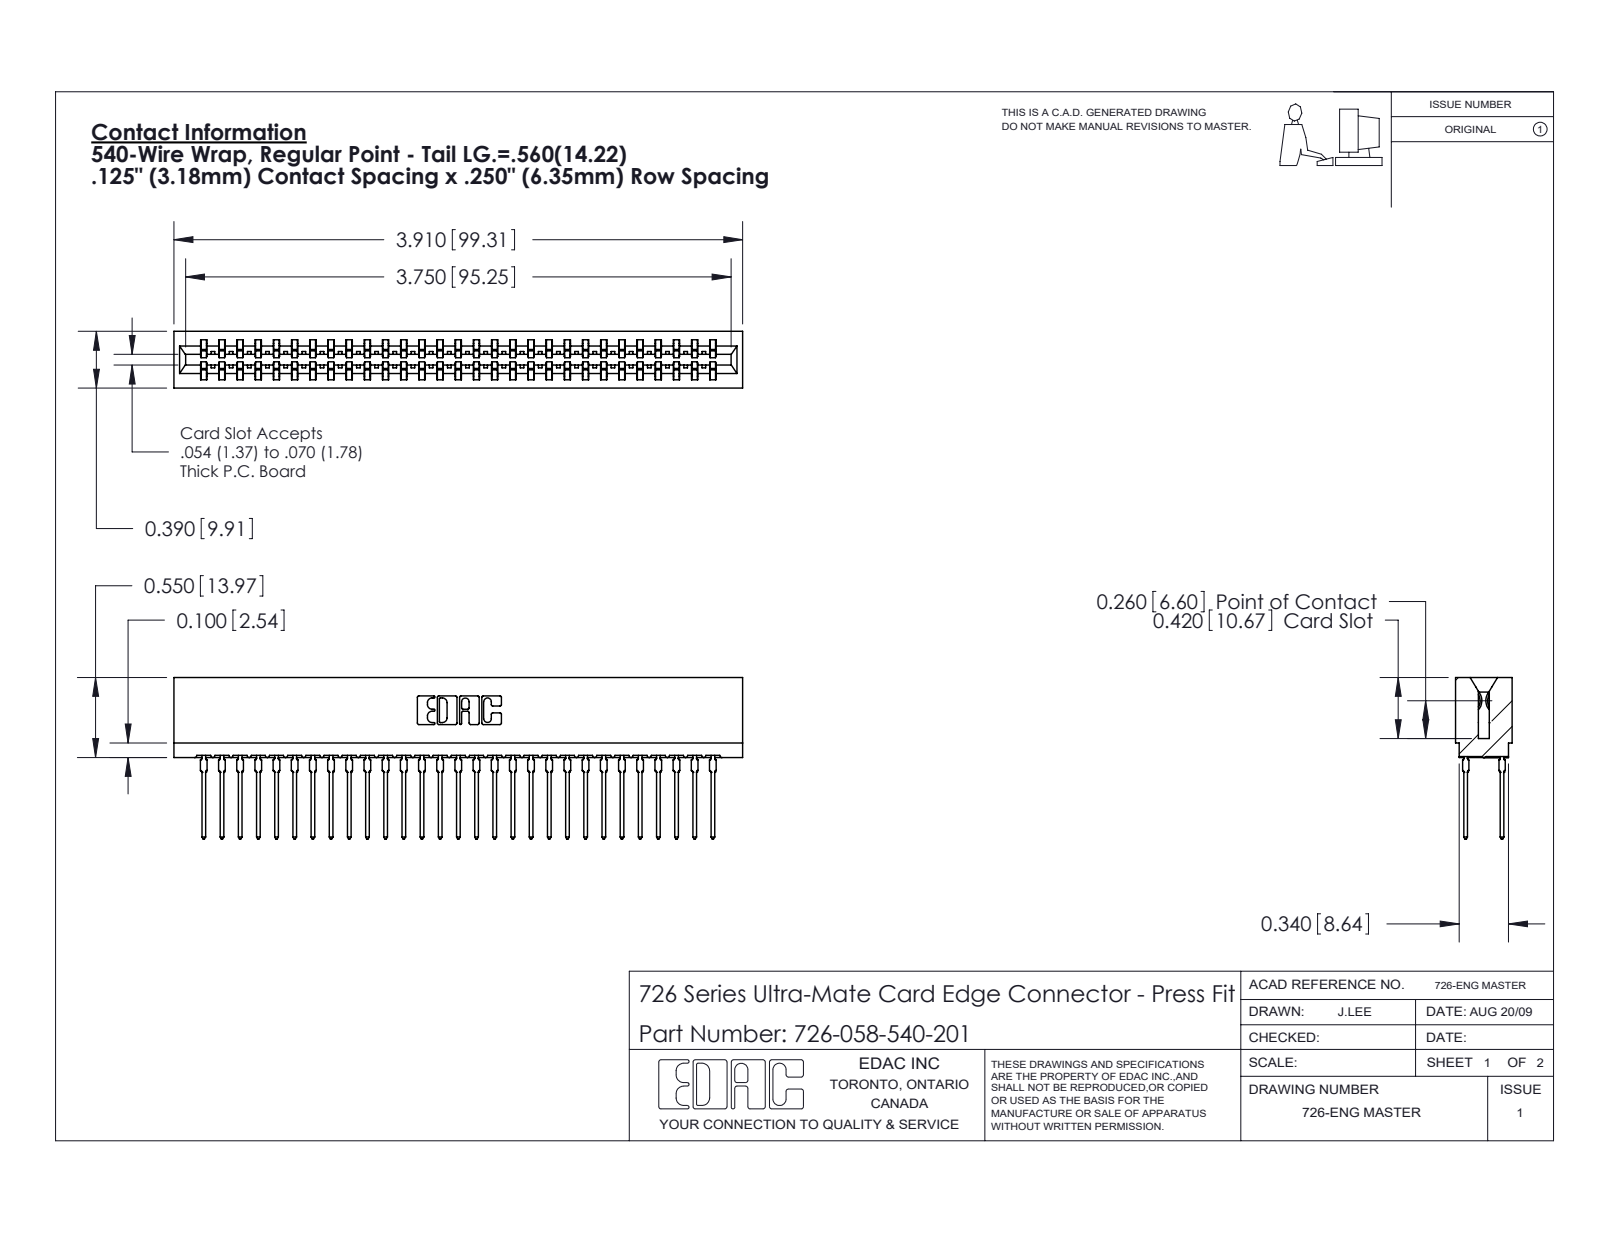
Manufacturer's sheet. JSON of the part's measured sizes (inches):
{"part_name": "746-292-001_540; 726-058-540-201; 726 Part_.515 Slot Depth - 01", "step_written_by": "SolidWorks 2020 (CONFIG_CONTROL_DESIGN)", "units": "inches", "bodies": {"solids": 59, "faces": 5288, "planar": 2723, "cylindrical": 1057, "other": 1508}, "overall_size": [3.91, 1.109, 0.39], "volume_in3": 0.573, "surface_area_in2": 25.14, "partial_cylinders_radius": [[0.021, 116], [0.015, 30], [0.01, 22], [0.005, 8], [0.011, 8], [0.007, 6], [0.031, 6], [0.026, 3]], "face_to_face_distances": [0.057, 0.333, 0.025, 0.307, 0.25, 0.39, 0.083, 0.275, 0.5, 0.75]}
